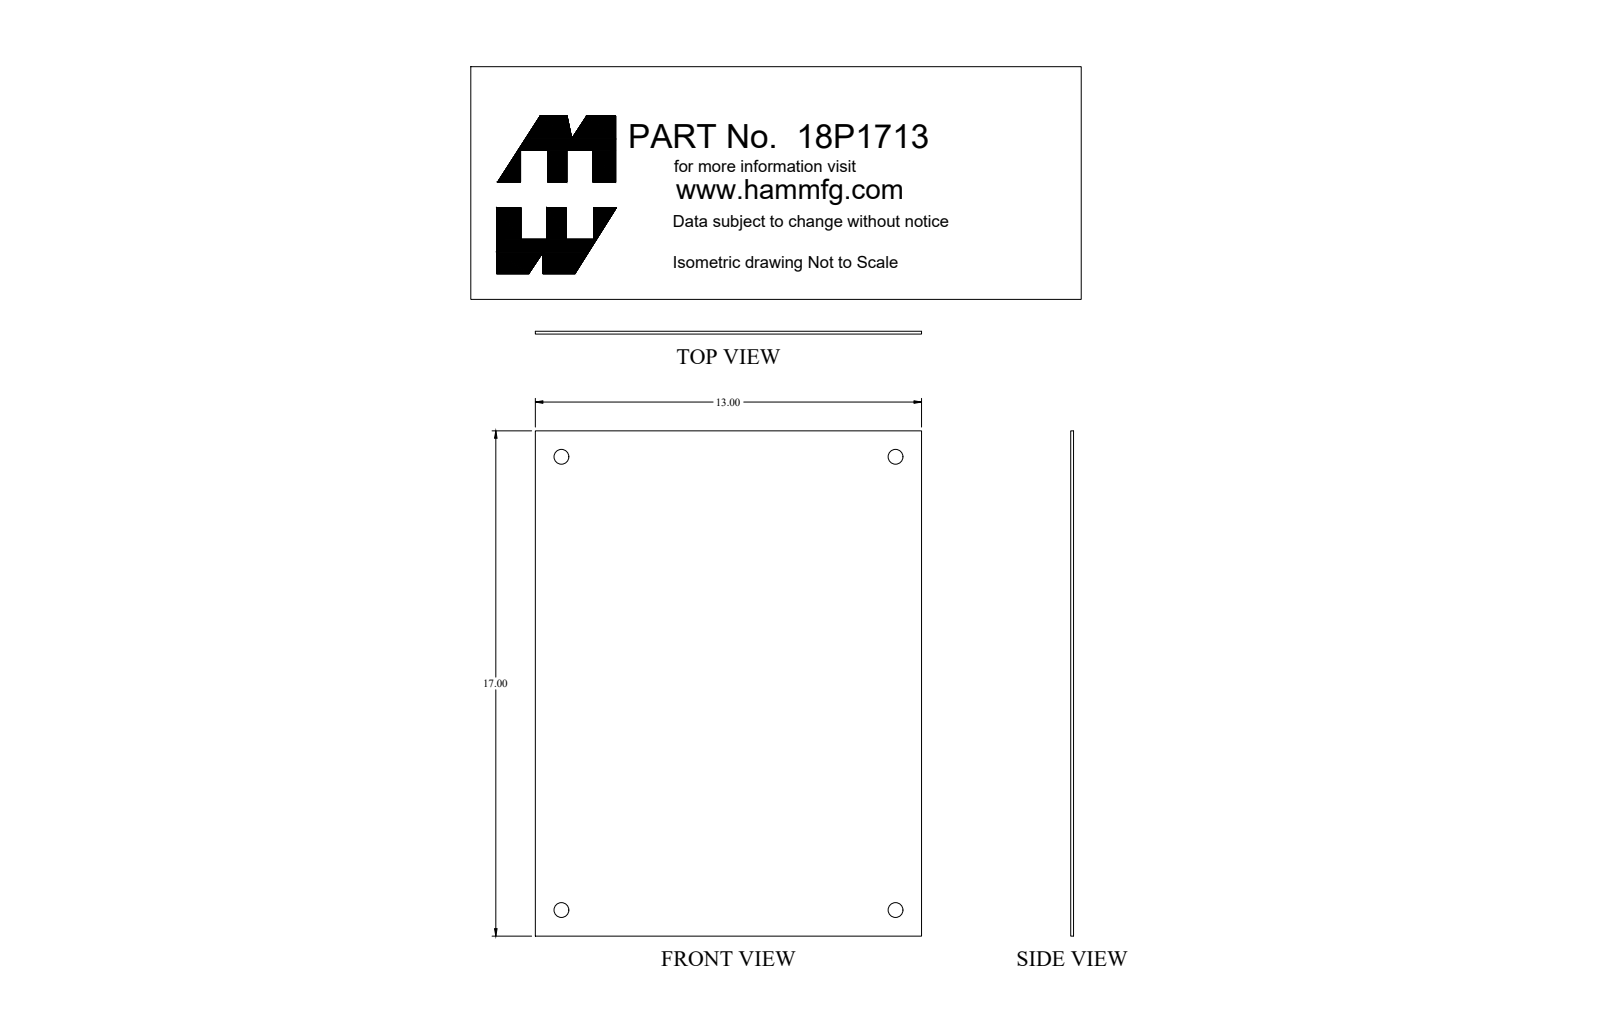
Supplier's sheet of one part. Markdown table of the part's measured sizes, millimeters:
| quantity | value |
| --- | --- |
| part name | 18P1713_Default |
| STEP written by | SolidWorks 2018 (CONFIG_CONTROL_DESIGN) |
| units | millimeters |
| bodies | 1 solid, 14 faces (6 planar, 8 cylindrical, 0 other) |
| overall size | 431.8 × 330.2 × 2.4 |
| volume | 342 800 mm³ |
| surface area | 288 200 mm² |
| round holes (diameter × count) | 12.7 × 4 |
| main face-to-face distances | 2.4, 330.2, 431.8 |
| hole center spacings | 285.8, 387.4, 481.4 |
